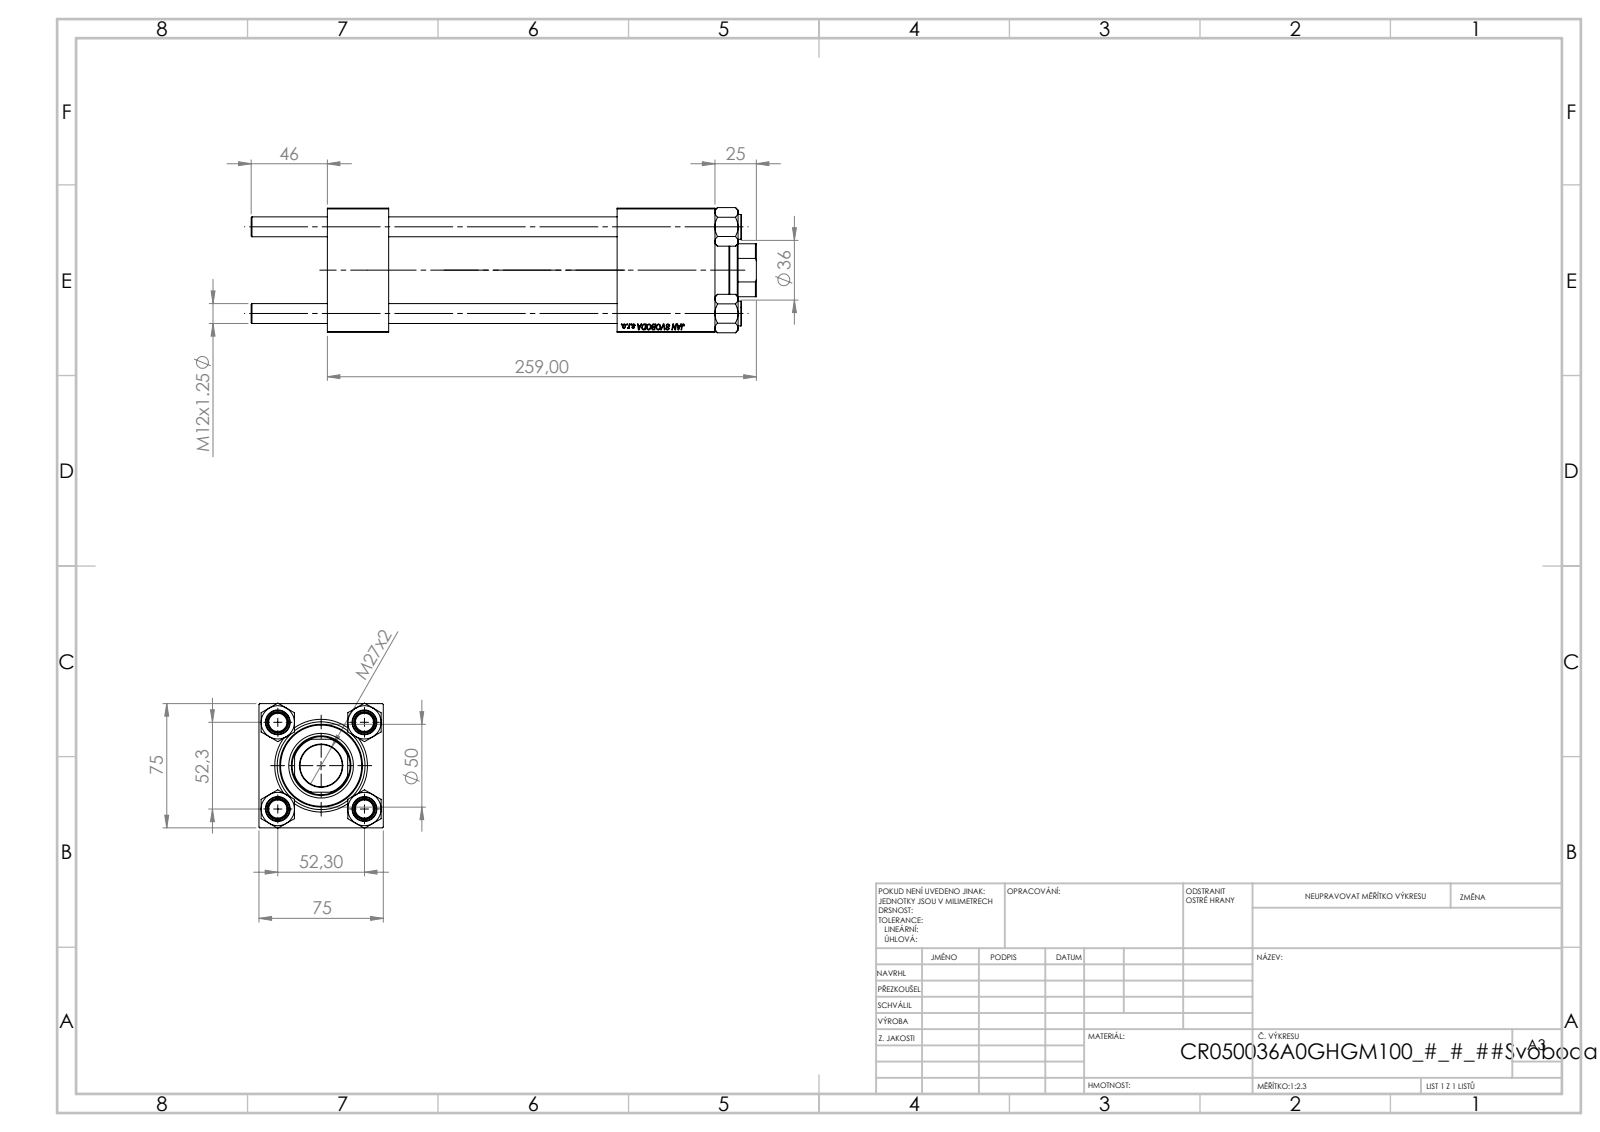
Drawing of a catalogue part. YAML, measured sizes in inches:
part_name: "V215CR_VCP; CR025_012_A_0_G_A_G_M_020_+#_##_TYCINKA; NUT_M5; V215CR_BODY_A (+1 more)"
step_written_by: "SolidWorks 2019 (CONFIG_CONTROL_DESIGN)"
units: inches
bodies: {solids: 11, faces: 1134, planar: 520, cylindrical: 78, other: 536}
overall_size: [12.008, 2.974, 2.953]
volume: 53.5
surface_area: 340.5
round_holes:
  - {diameter: 0.472, count: 4}
  - {diameter: 0.276, count: 2}
  - {diameter: 0.825, count: 2}
  - {diameter: 1.181, count: 2}
  - {diameter: 1.004, count: 1}
  - {diameter: 1.417, count: 1}
  - {diameter: 1.535, count: 1}
  - {diameter: 1.614, count: 1}
  - {diameter: 2.087, count: 1}
round_bosses_or_shafts:
  - {diameter: 0.591, count: 4}
  - {diameter: 2.205, count: 1}
  - {diameter: 1.969, count: 1}
partial_cylinders:
  - {radius: 0.689, count: 1}
face_to_face_distances: [2.953, 1.457, 6.89, 9.213, 7.756, 5.433, 2.323, 8.083, 6.626, 1.193]
hole_center_spacings: [1.456, 2.059, 2.912, 6.831]
